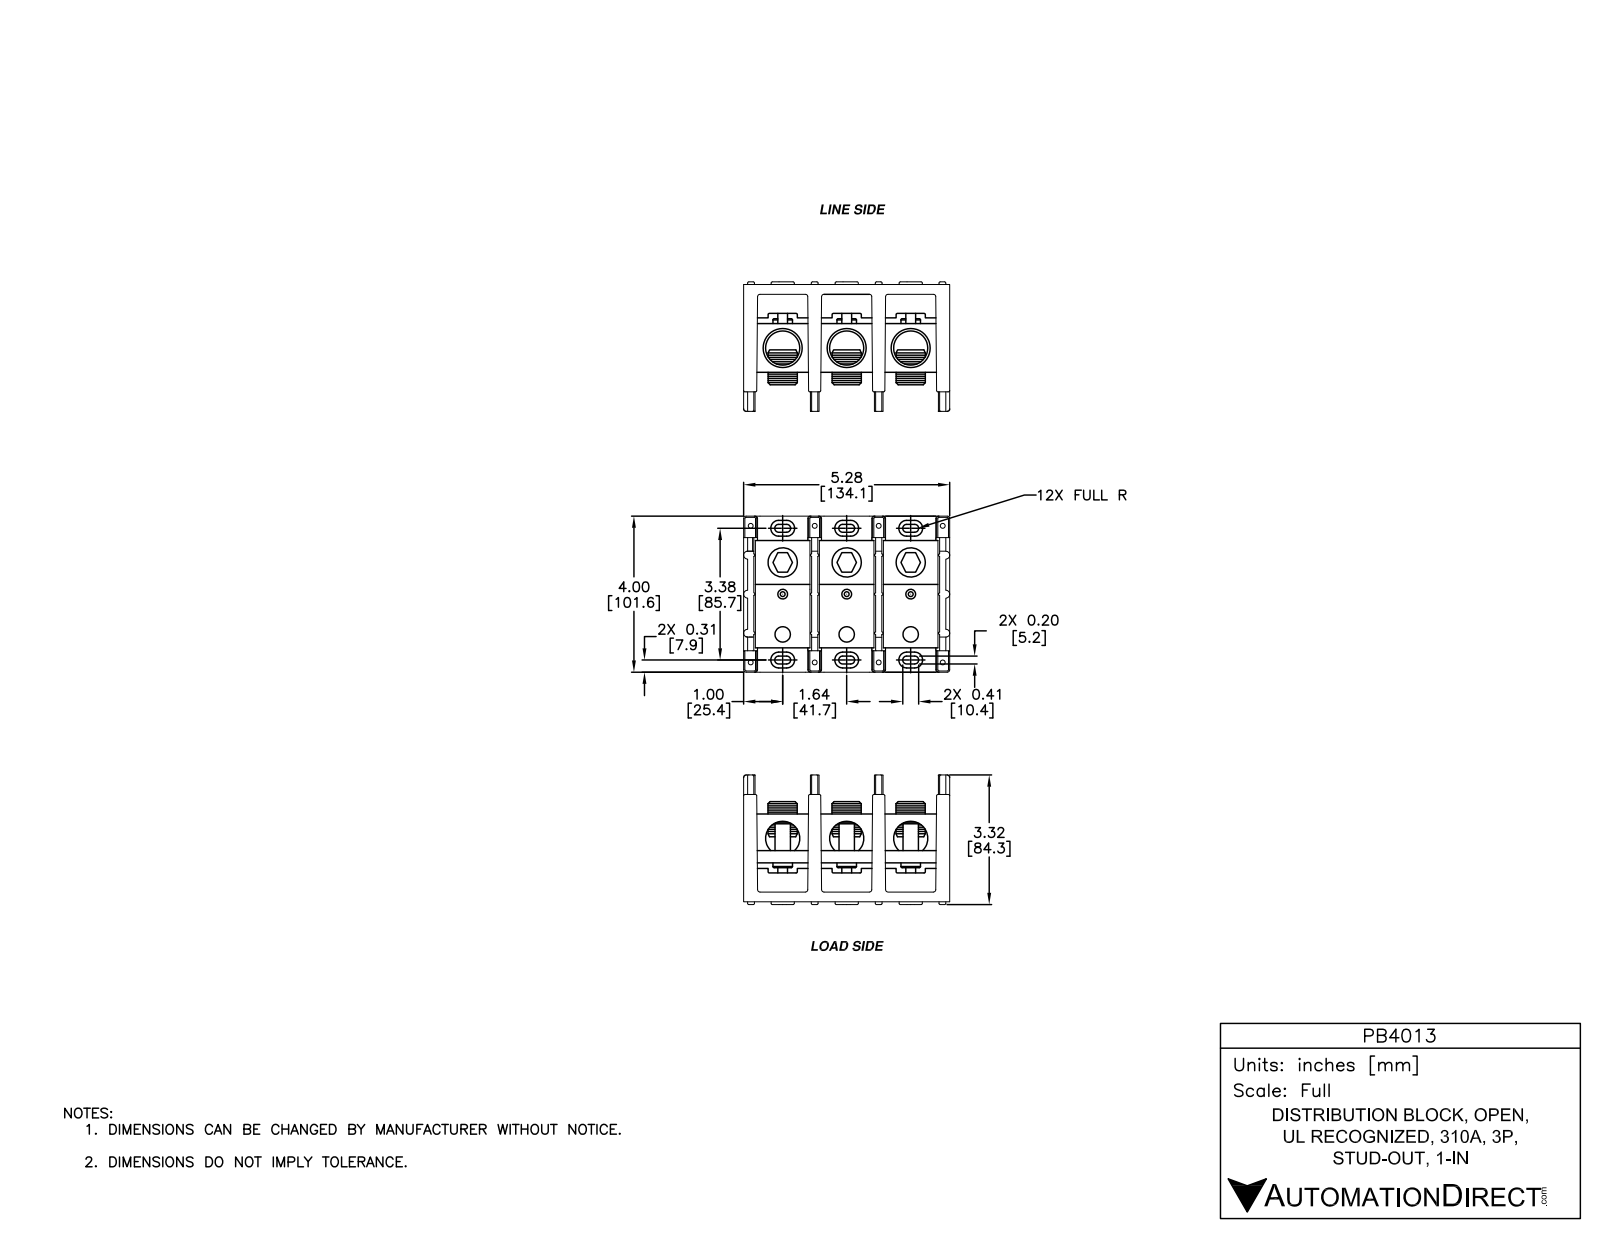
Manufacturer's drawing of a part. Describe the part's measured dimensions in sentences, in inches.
The part is named "PB4013". Its 3-D file was written by "SolidWorks 2014 (AUTOMOTIVE_DESIGN)". It is 16 solids with 1183 faces: 371 planar, 524 cylindrical and 288 other. Overall it measures 5.281 by 4 by 3.35 inches. Its volume is 22.07 cubic inches and its surface area 257 square inches. Round holes: 6 of diameter 0.125, 6 of diameter 0.75, 3 of diameter 0.25, 3 of diameter 0.5, 2 of diameter 0.125, 2 of diameter 0.395, 2 of diameter 0.875, 1 of diameter 0.395, 1 of diameter 0.875. Round bosses or shafts: 8 of diameter 0.174, 6 of diameter 0.062, 3 of diameter 0.5. Partial cylindrical surfaces (rounded edges, fillets, slot ends): 79 of radius 0.031, 54 of radius 0.1, 39 of radius 0.063, 25 of radius 0.203, 24 of radius 0.062, 12 of radius 0.094. The main face-to-face distances are 1.641, 3.281, 0.1, 0.259, 0.159, 1.741, 1.9, 1.481, 1.8, 4.922. The hole center spacings are 1.641, 1.933, 1.246, 2.691, 2.9, 3.02, 3.281, 1.091.
